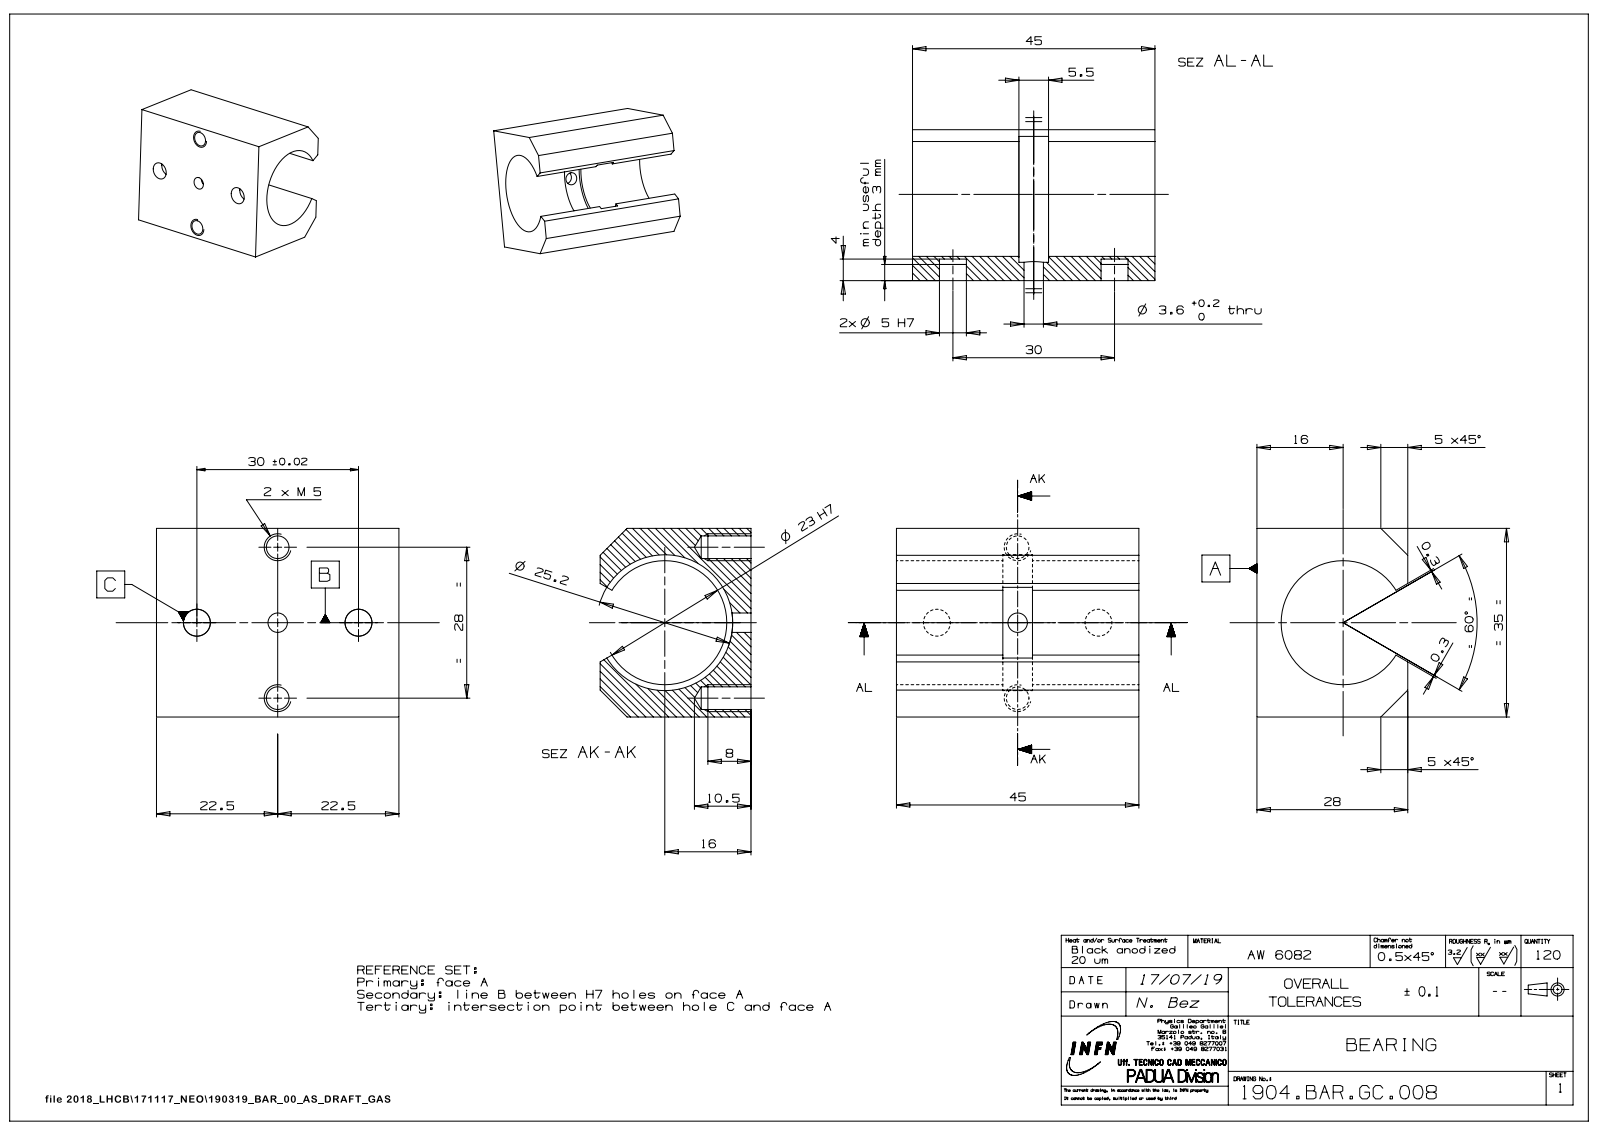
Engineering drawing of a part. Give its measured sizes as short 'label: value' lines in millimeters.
name: bmas477C8C18u67b
written by: SIEMENS PLM Software NX 12.0 (AUTOMOTIVE_DESIGN)
unit: mm
bodies: 1 solid, 25 faces (15 planar, 8 cylindrical, 2 other)
size: 45 × 35 × 28
volume: 22 750 mm³; area: 9 261 mm²
holes: 2× ⌀4.2, 2× ⌀5, 1× ⌀3.6, 1× ⌀23, 1× ⌀25.2
face distances: 35, 45, 28, 19.75, 25.25, 5.5, 24, 4
hole spacings: 20.52, 14, 15, 28, 30
